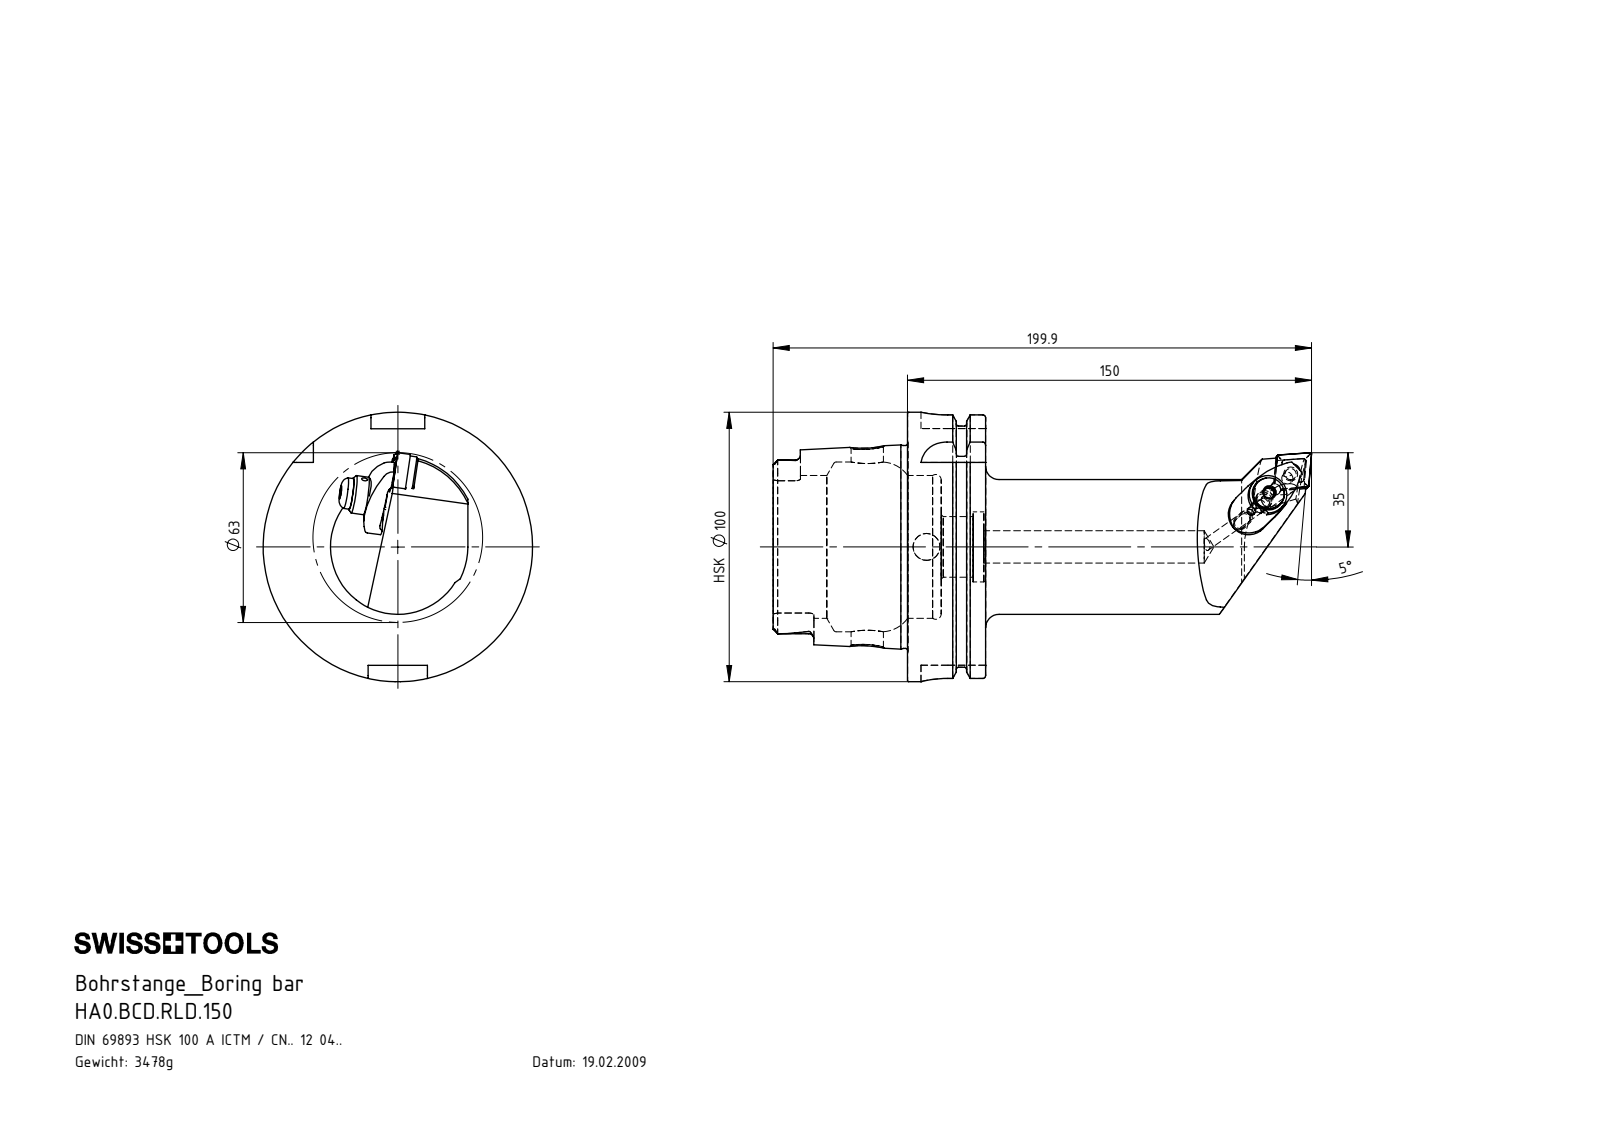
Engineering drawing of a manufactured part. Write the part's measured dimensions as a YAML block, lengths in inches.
part_name: "KVT_MB_600_050; WCC-ER5.102.012_B; HA0-BCD.RLD.150_A_Fertigbearbeitung; WCC-ER5.102.005_A (+6 more)"
step_written_by: "SolidWorks 2017 (AUTOMOTIVE_DESIGN)"
units: inches
bodies: {solids: 10, faces: 452, planar: 114, cylindrical: 150, other: 188}
overall_size: [7.87, 3.937, 3.937]
volume: 26.99
surface_area: 116.2
round_holes:
  - {diameter: 0.079, count: 3}
  - {diameter: 0.165, count: 3}
  - {diameter: 0.197, count: 2}
  - {diameter: 0.276, count: 2}
  - {diameter: 0.472, count: 2}
  - {diameter: 0.118, count: 1}
  - {diameter: 0.157, count: 1}
  - {diameter: 0.203, count: 1}
  - {diameter: 0.244, count: 1}
  - {diameter: 0.258, count: 1}
  - {diameter: 0.335, count: 1}
  - {diameter: 0.394, count: 1}
round_bosses_or_shafts:
  - {diameter: 0.197, count: 2}
  - {diameter: 3.937, count: 1}
  - {diameter: 3.62, count: 1}
  - {diameter: 2.963, count: 1}
  - {diameter: 1.969, count: 1}
  - {diameter: 0.551, count: 1}
  - {diameter: 0.453, count: 1}
  - {diameter: 0.276, count: 1}
partial_cylinders:
  - {radius: 0.015, count: 6}
  - {radius: 0.027, count: 6}
  - {radius: 0.075, count: 6}
  - {radius: 0.016, count: 4}
  - {radius: 0.039, count: 4}
  - {radius: 0.394, count: 4}
  - {radius: 0.059, count: 3}
  - {radius: 0.079, count: 2}
face_to_face_distances: [1.14, 0.49, 0.65, 1.965, 2.455, 3.104, 3.457, 3.079, 1.114, 0.624]
hole_center_spacings: [0.315, 0.588, 0.591, 0.255, 0.263, 0.263, 0.323, 0.325]
